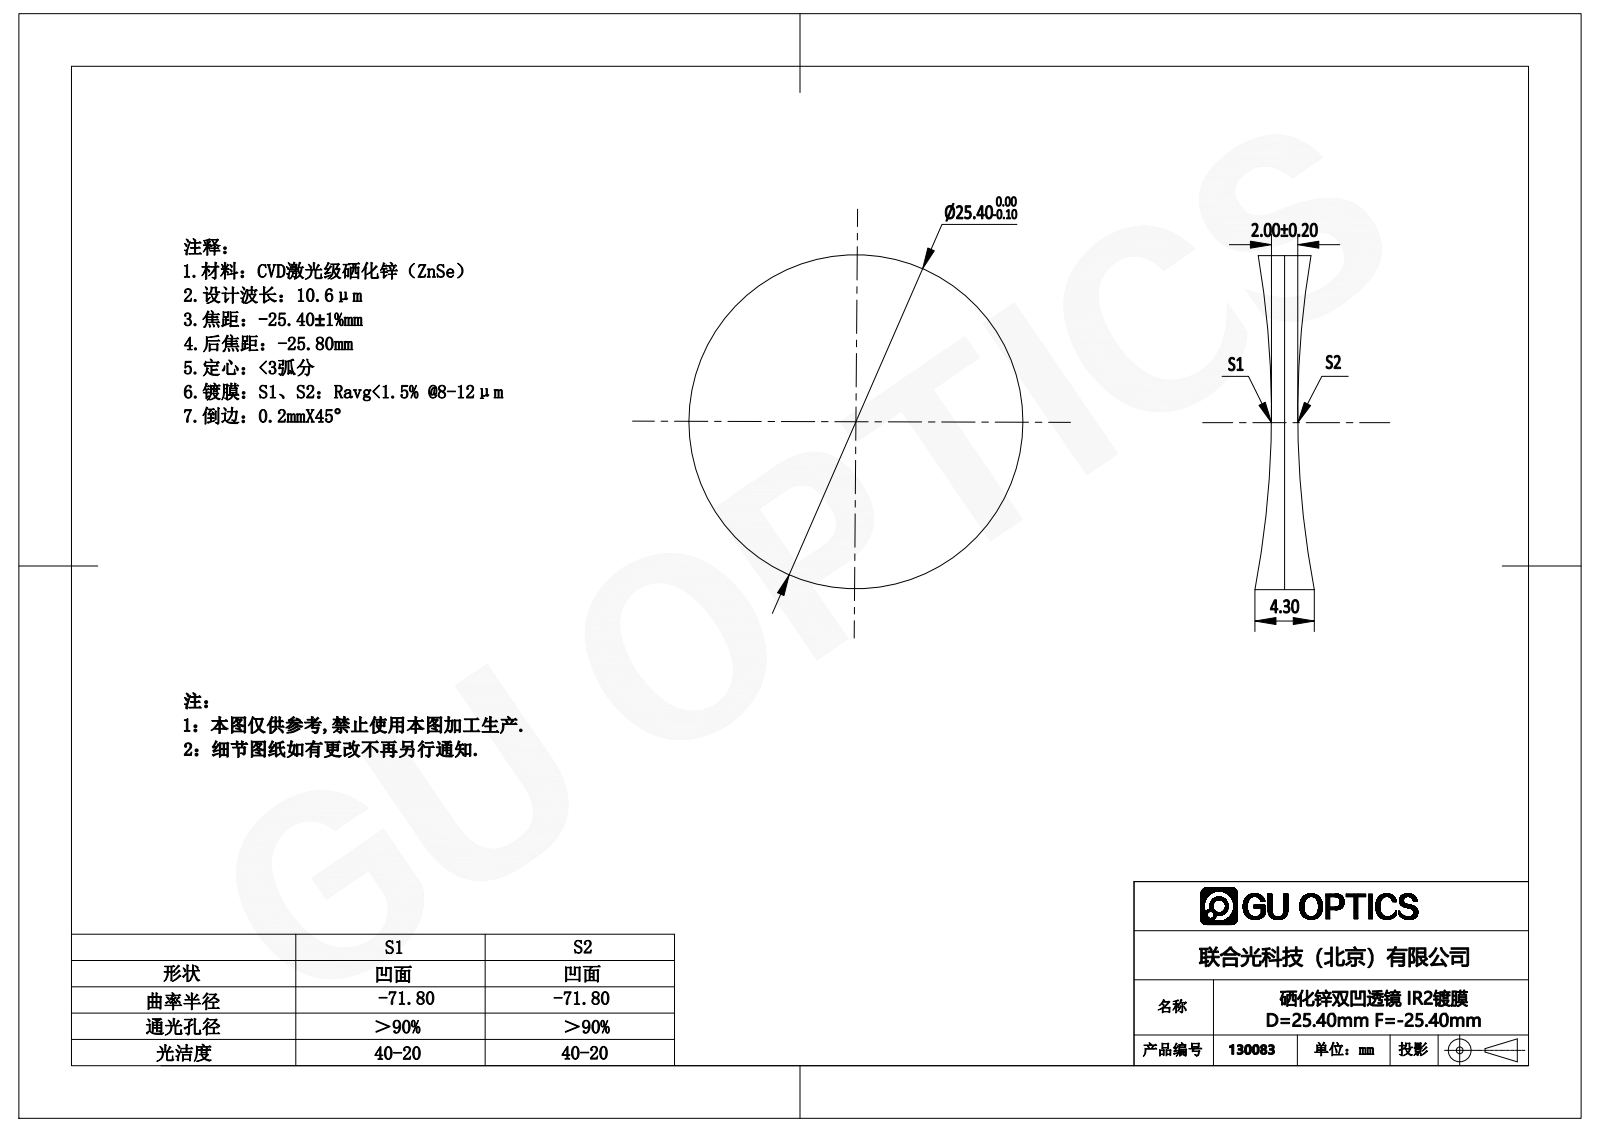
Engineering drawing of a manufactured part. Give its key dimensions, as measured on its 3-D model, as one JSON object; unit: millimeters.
{"part_name": "130078", "step_written_by": "SolidWorks 2016 (AUTOMOTIVE_DESIGN)", "units": "millimeters", "bodies": {"solids": 1, "faces": 6, "planar": 0, "cylindrical": 2, "other": 4}, "overall_size": [25.4, 25.4, 4.01], "volume_mm3": 1501, "surface_area_mm2": 1341, "round_bosses_or_shafts": [[25.4, 1]]}
